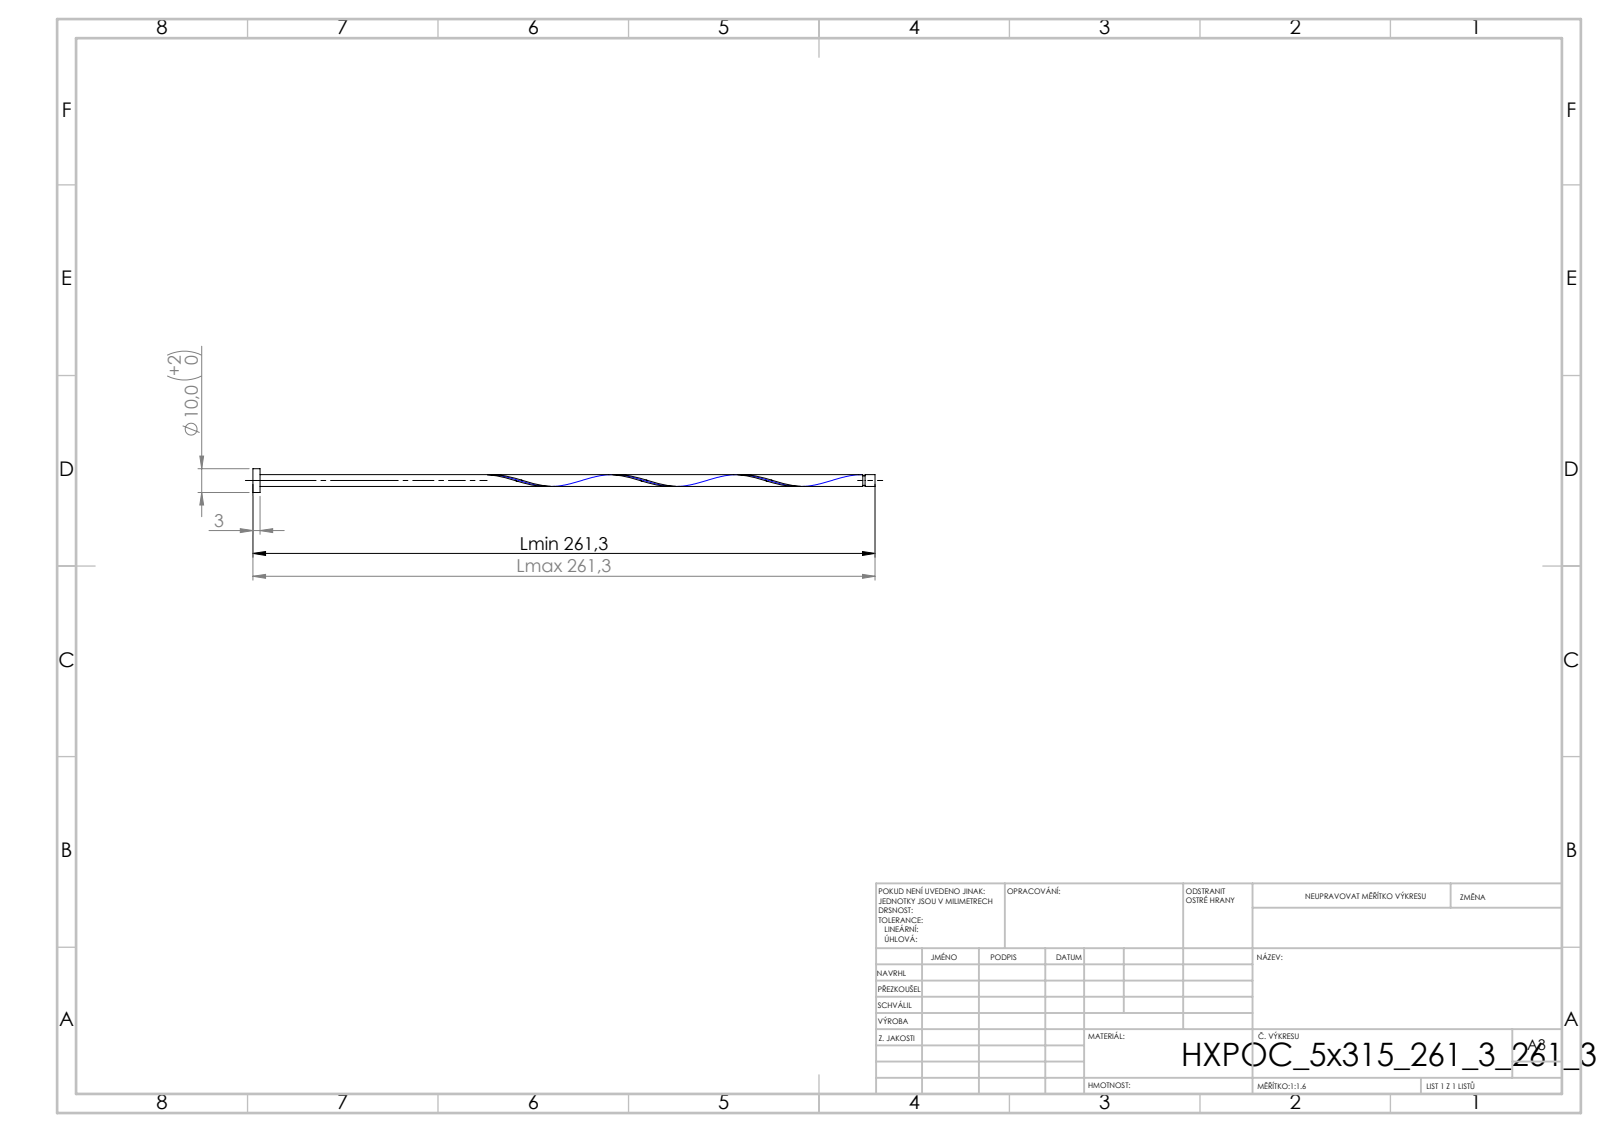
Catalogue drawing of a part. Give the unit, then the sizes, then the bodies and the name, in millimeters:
Units: millimetres
Overall size (bounding box): 261.3 × 10 × 10
Round bosses / shafts (diameter × count): ⌀10 ×1, ⌀5 ×1, ⌀4 ×1
Main face-to-face distances: 3, 261.3, 258.3, 257.14, 254.14, 4.16, 256.14, 253.14, 1, 5.16
Volume: 6 615 mm³ · Surface area: 6 047 mm²
Bodies: 1 solid, 16 faces (6 planar, 9 cylindrical, 1 other)
STEP written by: SolidWorks 2019 (CONFIG_CONTROL_DESIGN)
